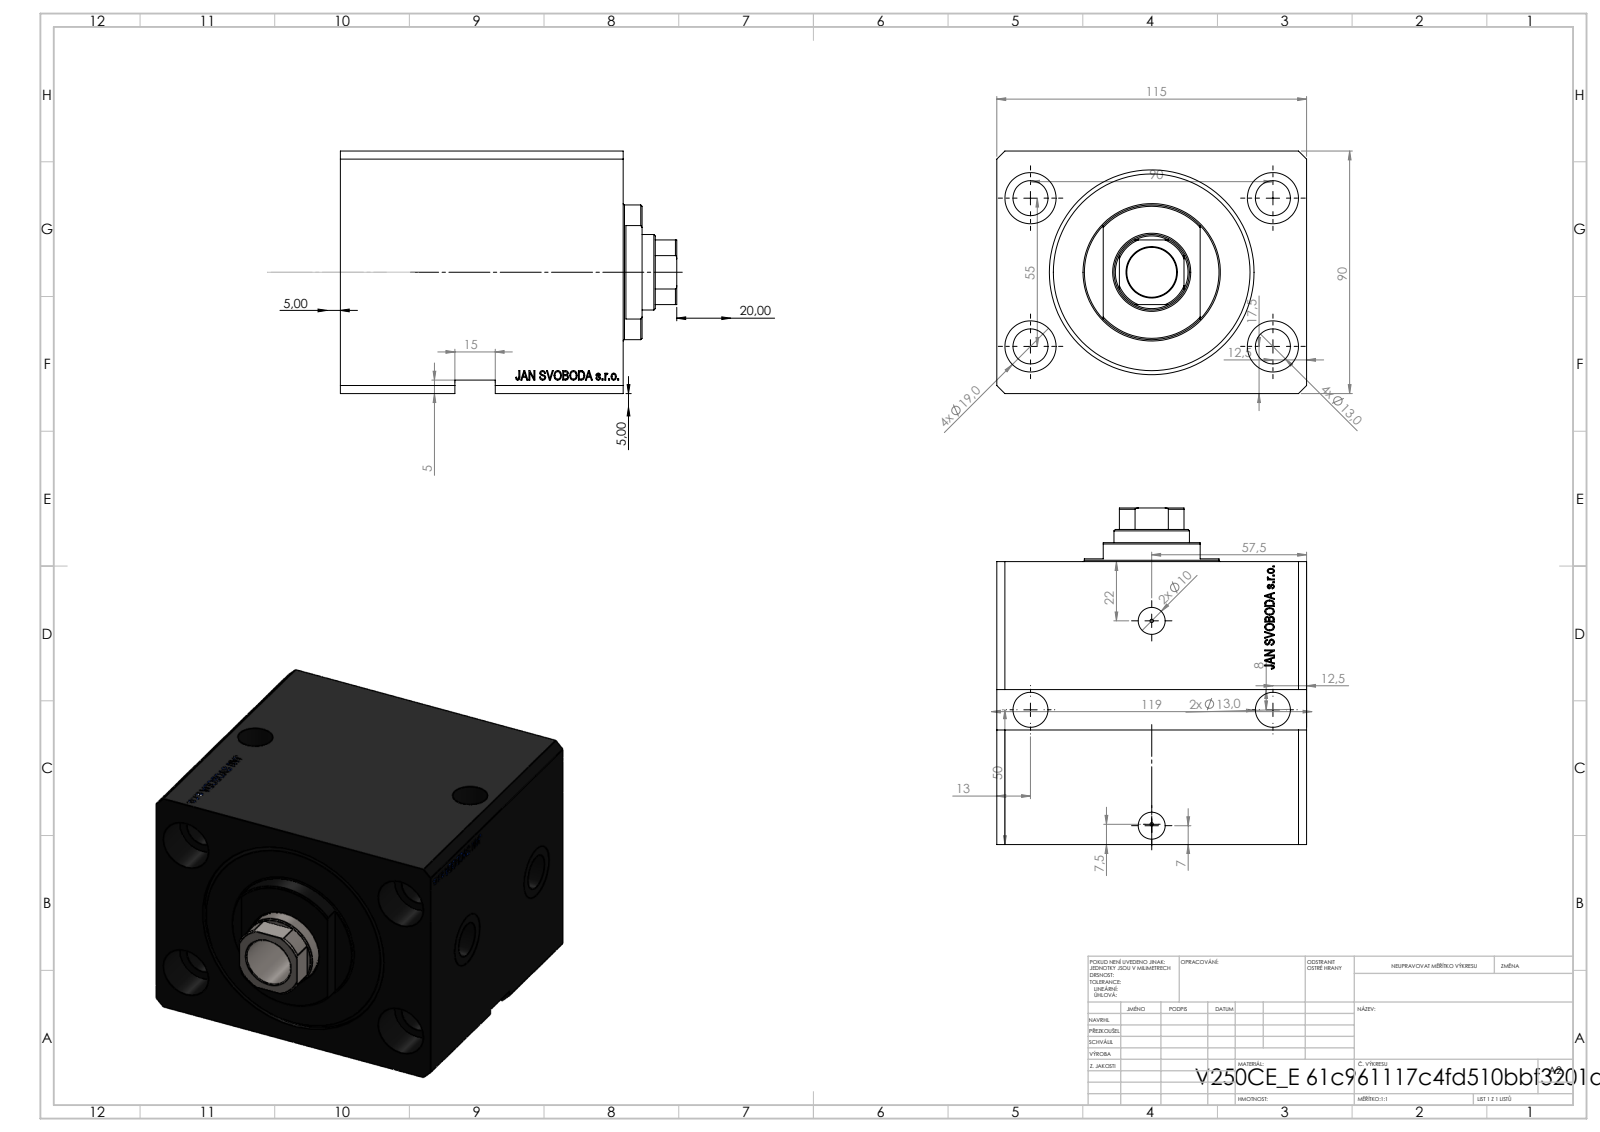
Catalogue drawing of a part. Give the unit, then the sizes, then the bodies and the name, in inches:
Units: inches
Overall size (bounding box): 4.921 × 4.528 × 3.543
Round holes (diameter × count): ⌀0.512 ×6, ⌀0.049 ×4, ⌀0.748 ×4, ⌀0.394 ×2, ⌀0.518 ×2, ⌀0.787 ×2, ⌀0.728 ×1, ⌀1.102 ×1, ⌀2.48 ×1, ⌀2.992 ×1
Round bosses / shafts (diameter × count): ⌀1.969 ×1
Partial cylindrical surfaces — rounded edges, fillets, slot ends (radius × count): R0.531 ×1
Main face-to-face distances: 3.543, 0.787, 4.528, 3.346, 4.134, 3.429, 0.705, 2.642, 1.575, 2.559
Hole centre spacings: 2.076, 2.165, 3.543, 2.197, 2.436, 2.45, 4.153, 0.021
Volume: 57.54 in³ · Surface area: 223.5 in²
Bodies: 3 solids, 937 faces (467 planar, 84 cylindrical, 386 other)
Part name (STEP PRODUCT): V250CE_C_VCP; V250CE_VC_E; V250CE_E_Body
STEP written by: SolidWorks 2019 (CONFIG_CONTROL_DESIGN)
